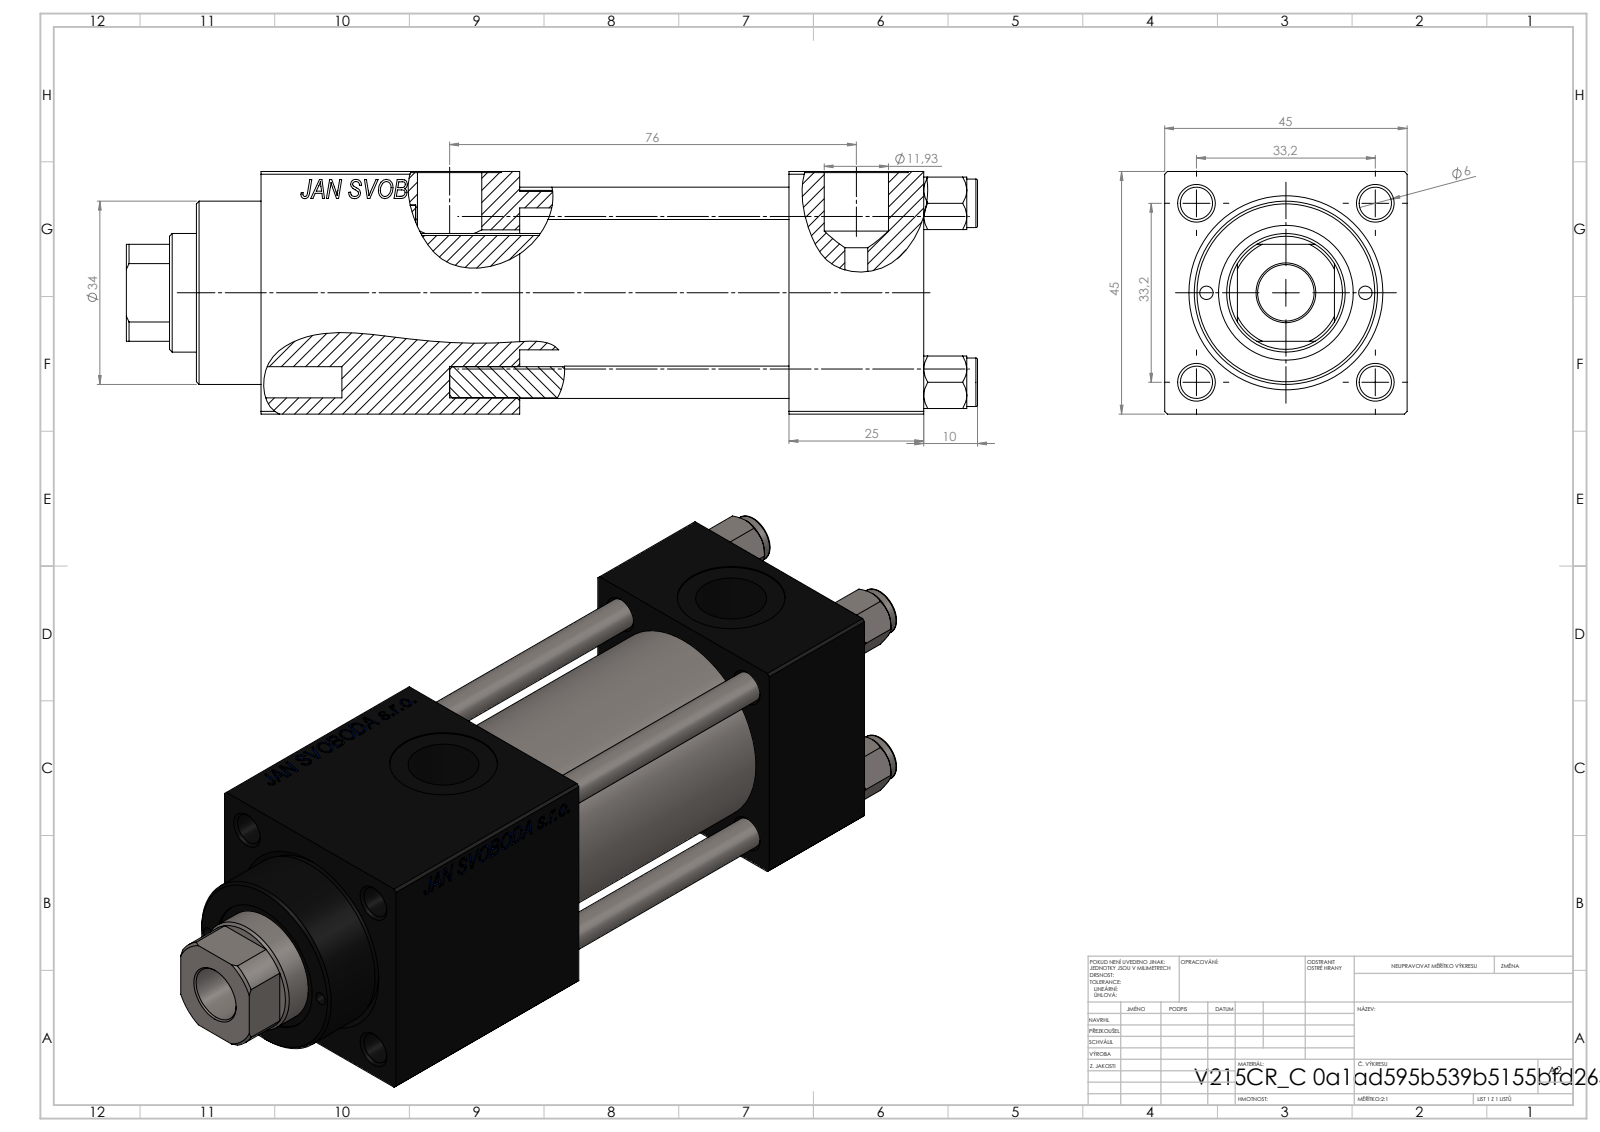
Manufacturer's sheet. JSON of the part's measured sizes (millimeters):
{"part_name": "V215_VC_A; V215CR_VCP_C; NUT_M5_C; V215CR_C_TYCINKA (+1 more)", "step_written_by": "SolidWorks 2019 (CONFIG_CONTROL_DESIGN)", "units": "millimeters", "bodies": {"solids": 11, "faces": 1154, "planar": 527, "cylindrical": 91, "other": 536}, "overall_size": [158, 45, 45], "volume_mm3": 209612, "surface_area_mm2": 71570, "round_holes": [[6, 4], [2.5, 2], [7, 2], [13.16, 2], [20, 2], [10.5, 1], [22, 1], [24, 1], [25, 1], [32, 1], [33, 1]], "round_bosses_or_shafts": [[9, 4], [38, 1], [34, 1]], "partial_cylinders_radius": [[10.5, 1]], "face_to_face_distances": [45, 25, 50, 123, 75, 98, 48, 94.3, 69.3, 19.3], "hole_center_spacings": [16.7, 23.48, 33.2, 35.47, 14.75, 46.95, 29.5, 75.5]}
